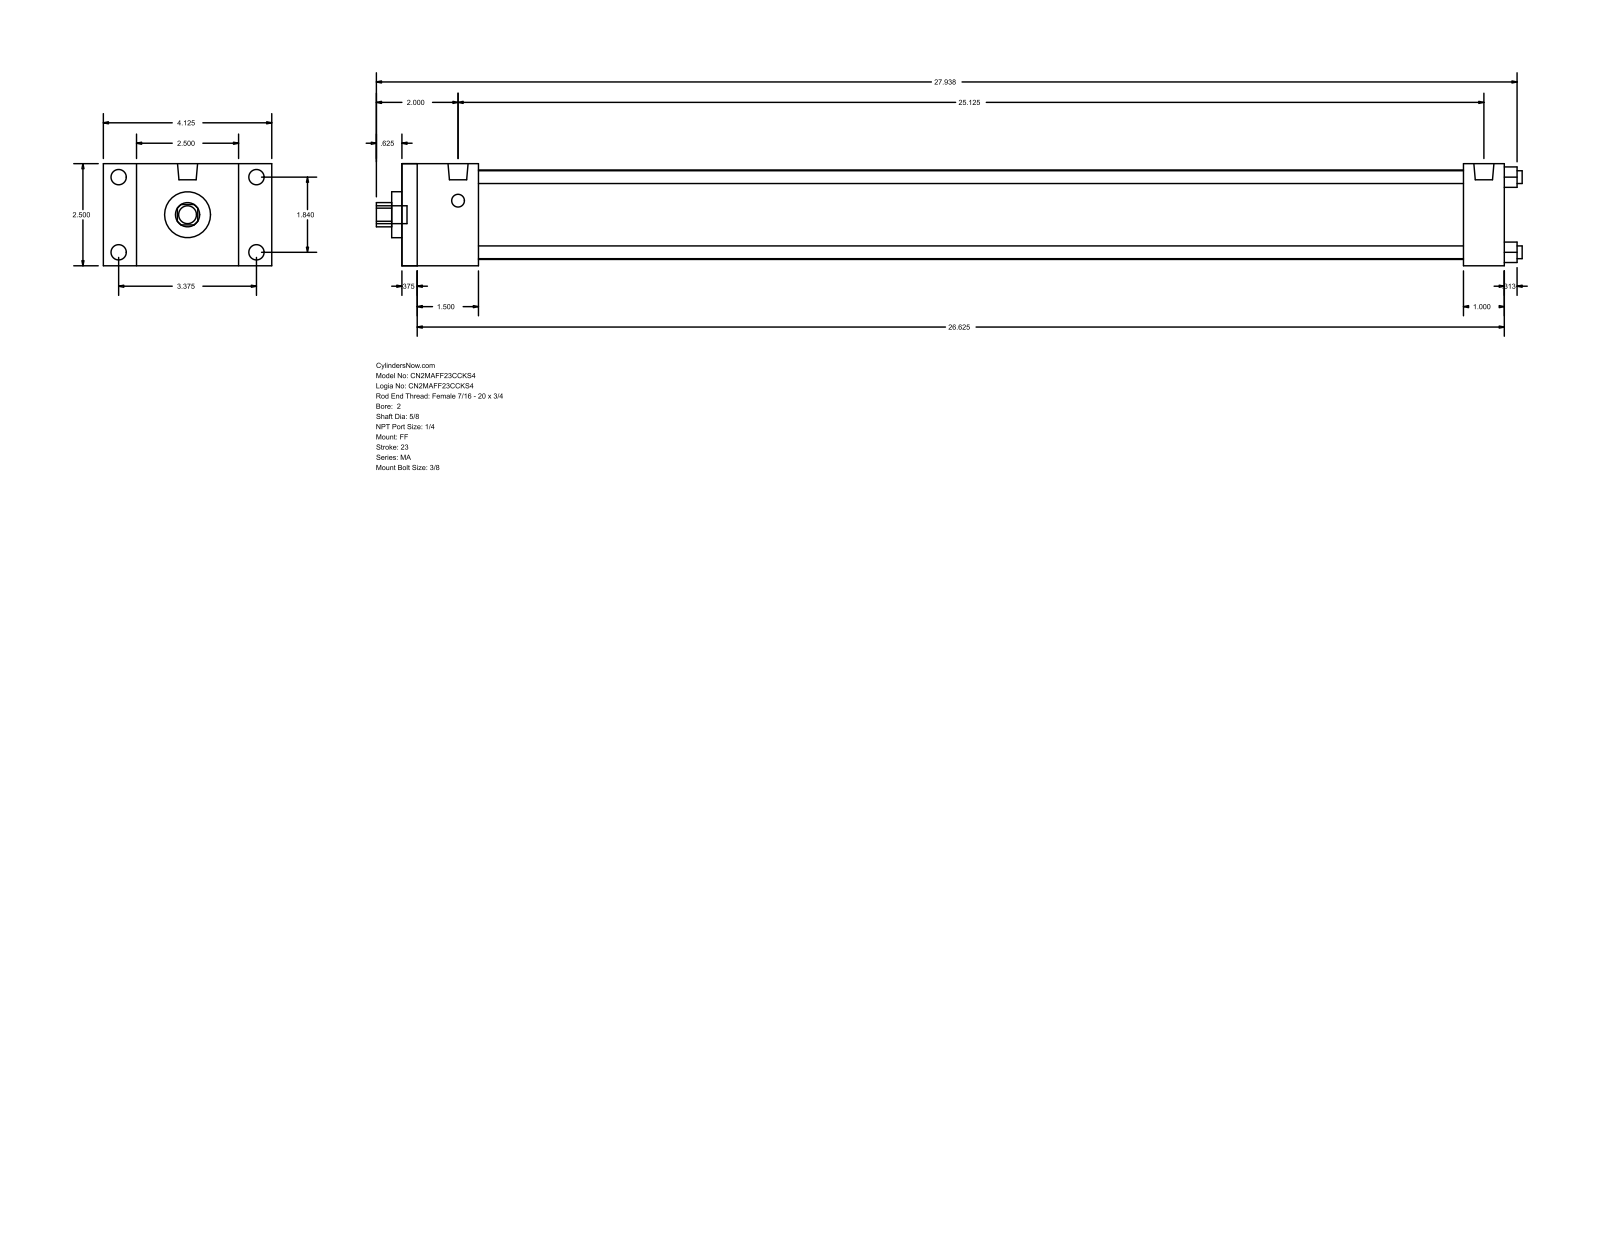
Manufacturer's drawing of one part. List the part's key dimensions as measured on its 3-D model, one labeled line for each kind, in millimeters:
Part name (STEP PRODUCT): MA_FF__0200_0.625
STEP written by: GSSL Pune (CONFIG_CONTROL_DESIGN)
Units: millimetres
Bodies: 0 solids, 92 faces (64 planar, 28 cylindrical, 0 other)
Overall size (bounding box): 712.79 × 104.78 × 63.5
Round holes (diameter × count): ⌀7.94 ×4, ⌀15.88 ×1, ⌀28.57 ×1, ⌀55.63 ×1
Round bosses / shafts (diameter × count): ⌀9.53 ×4, ⌀7.94 ×4, ⌀12.49 ×2, ⌀11.11 ×1
Partial cylindrical surfaces — rounded edges, fillets, slot ends (radius × count): R7.54 ×1
Main face-to-face distances: 63.5, 685.79, 9.52, 676.27, 25.4, 38.1, 47.62, 660.39, 650.87, 612.77
Hole centre spacings: 33.05, 46.74, 66.1
